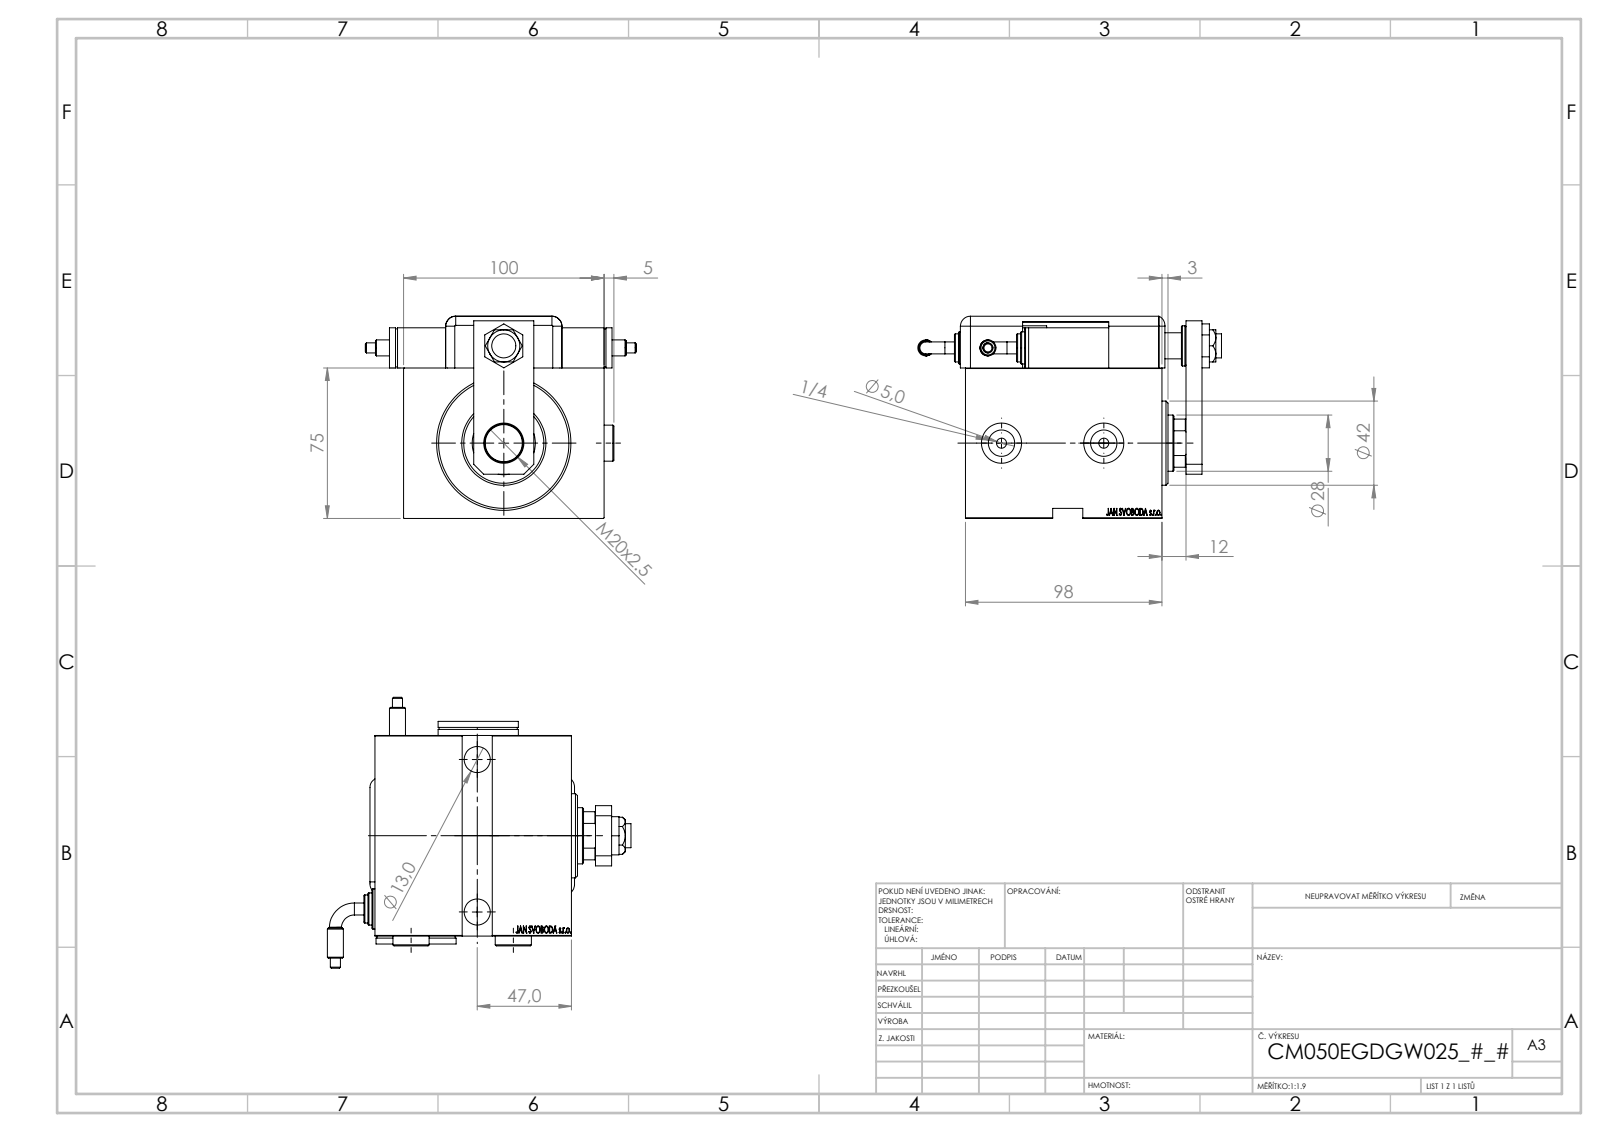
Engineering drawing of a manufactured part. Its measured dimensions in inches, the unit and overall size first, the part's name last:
Units: inches
Overall size (bounding box): 5.963 × 5.315 × 3.969
Round holes (diameter × count): ⌀0.512 ×3, ⌀0.787 ×3, ⌀0.157 ×2, ⌀0.197 ×2, ⌀0.315 ×2, ⌀0.518 ×2, ⌀0.748 ×2, ⌀0.472 ×1, ⌀0.551 ×1, ⌀0.728 ×1, ⌀1.102 ×1, ⌀1.24 ×1
Round bosses / shafts (diameter × count): ⌀0.787 ×3, ⌀0.709 ×2, ⌀0.63 ×2, ⌀0.551 ×2, ⌀0.315 ×2, ⌀0.236 ×2, ⌀0.198 ×2, ⌀2.047 ×1
Partial cylindrical surfaces — rounded edges, fillets, slot ends (radius × count): R0.197 ×9, R0.394 ×1, R0.531 ×1
Main face-to-face distances: 0.118, 2.953, 3.858, 3.937, 0.551, 0.787, 3.307, 3.11, 3.969, 1.016
Hole centre spacings: 1.858, 2.41, 0.787, 1.909, 2.008, 2.992
Volume: 49.78 in³ · Surface area: 242.7 in²
Bodies: 15 solids, 1314 faces (654 planar, 123 cylindrical, 537 other)
Part name (STEP PRODUCT): SWITCH DIM A_G; V450CM_VC_B; Zatka_OIL_PORT; NUT_D19 (+7 more)
STEP written by: SolidWorks 2019 (CONFIG_CONTROL_DESIGN)
